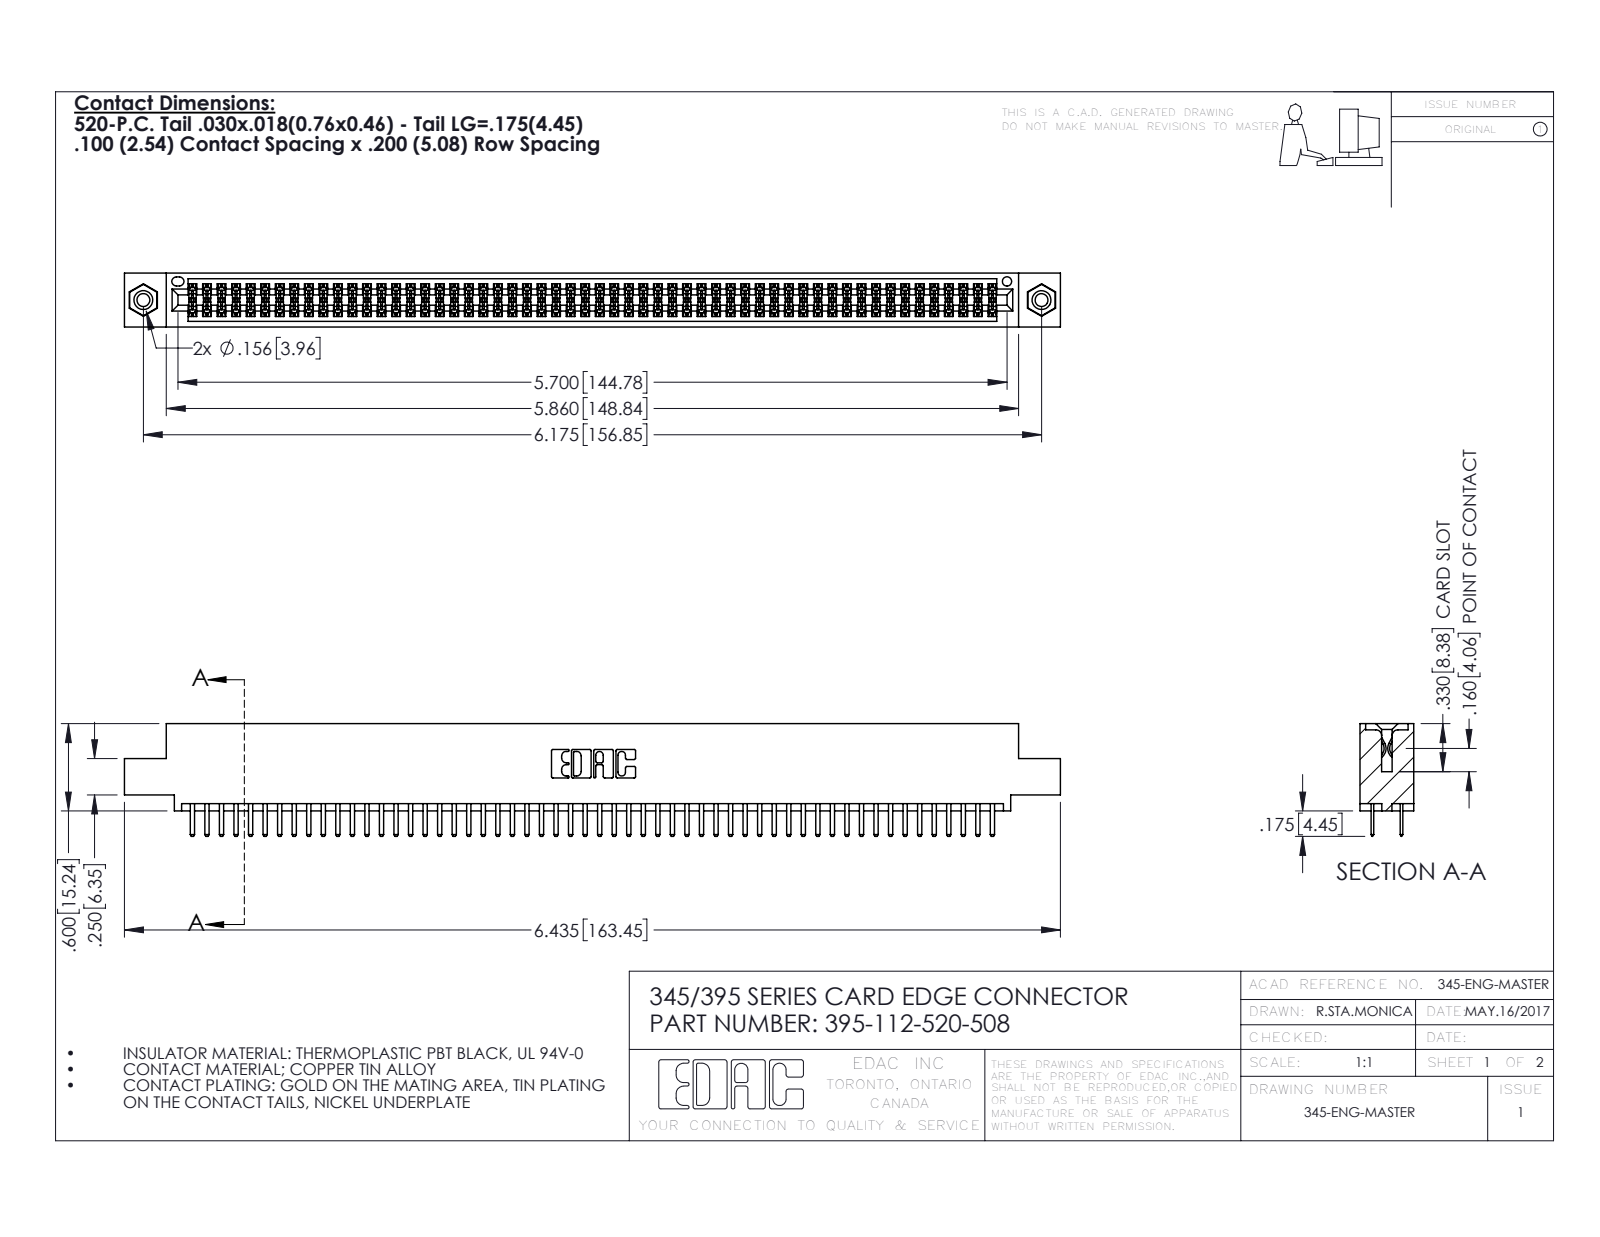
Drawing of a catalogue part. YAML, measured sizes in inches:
part_name: "395-112-520-508; 345-250-001_345-250-003-102; 345 Part_0.110 Offset - 0.156 Dia-TI; 345-292-001_345-293-120"
step_written_by: "SolidWorks 2016 (CONFIG_CONTROL_DESIGN)"
units: inches
bodies: {solids: 115, faces: 6238, planar: 4036, cylindrical: 2186, other: 16}
overall_size: [6.435, 0.775, 0.37]
volume: 0.969
surface_area: 36.8
round_holes:
  - {diameter: 0.089, count: 2}
  - {diameter: 0.125, count: 2}
  - {diameter: 0.156, count: 2}
  - {diameter: 0.064, count: 1}
round_bosses_or_shafts:
  - {diameter: 0.155, count: 2}
partial_cylinders:
  - {radius: 0.006, count: 168}
  - {radius: 0.01, count: 116}
  - {radius: 0.01, count: 22}
  - {radius: 0.007, count: 6}
  - {radius: 0.031, count: 6}
  - {radius: 0.026, count: 3}
  - {radius: 0.014, count: 2}
  - {radius: 0.019, count: 2}
face_to_face_distances: [0.072, 0.298, 0.2, 0.37, 0.098, 0.272, 0.025, 0.225, 0.022, 0.072]
hole_center_spacings: [0.27, 5.939, 6.175]
